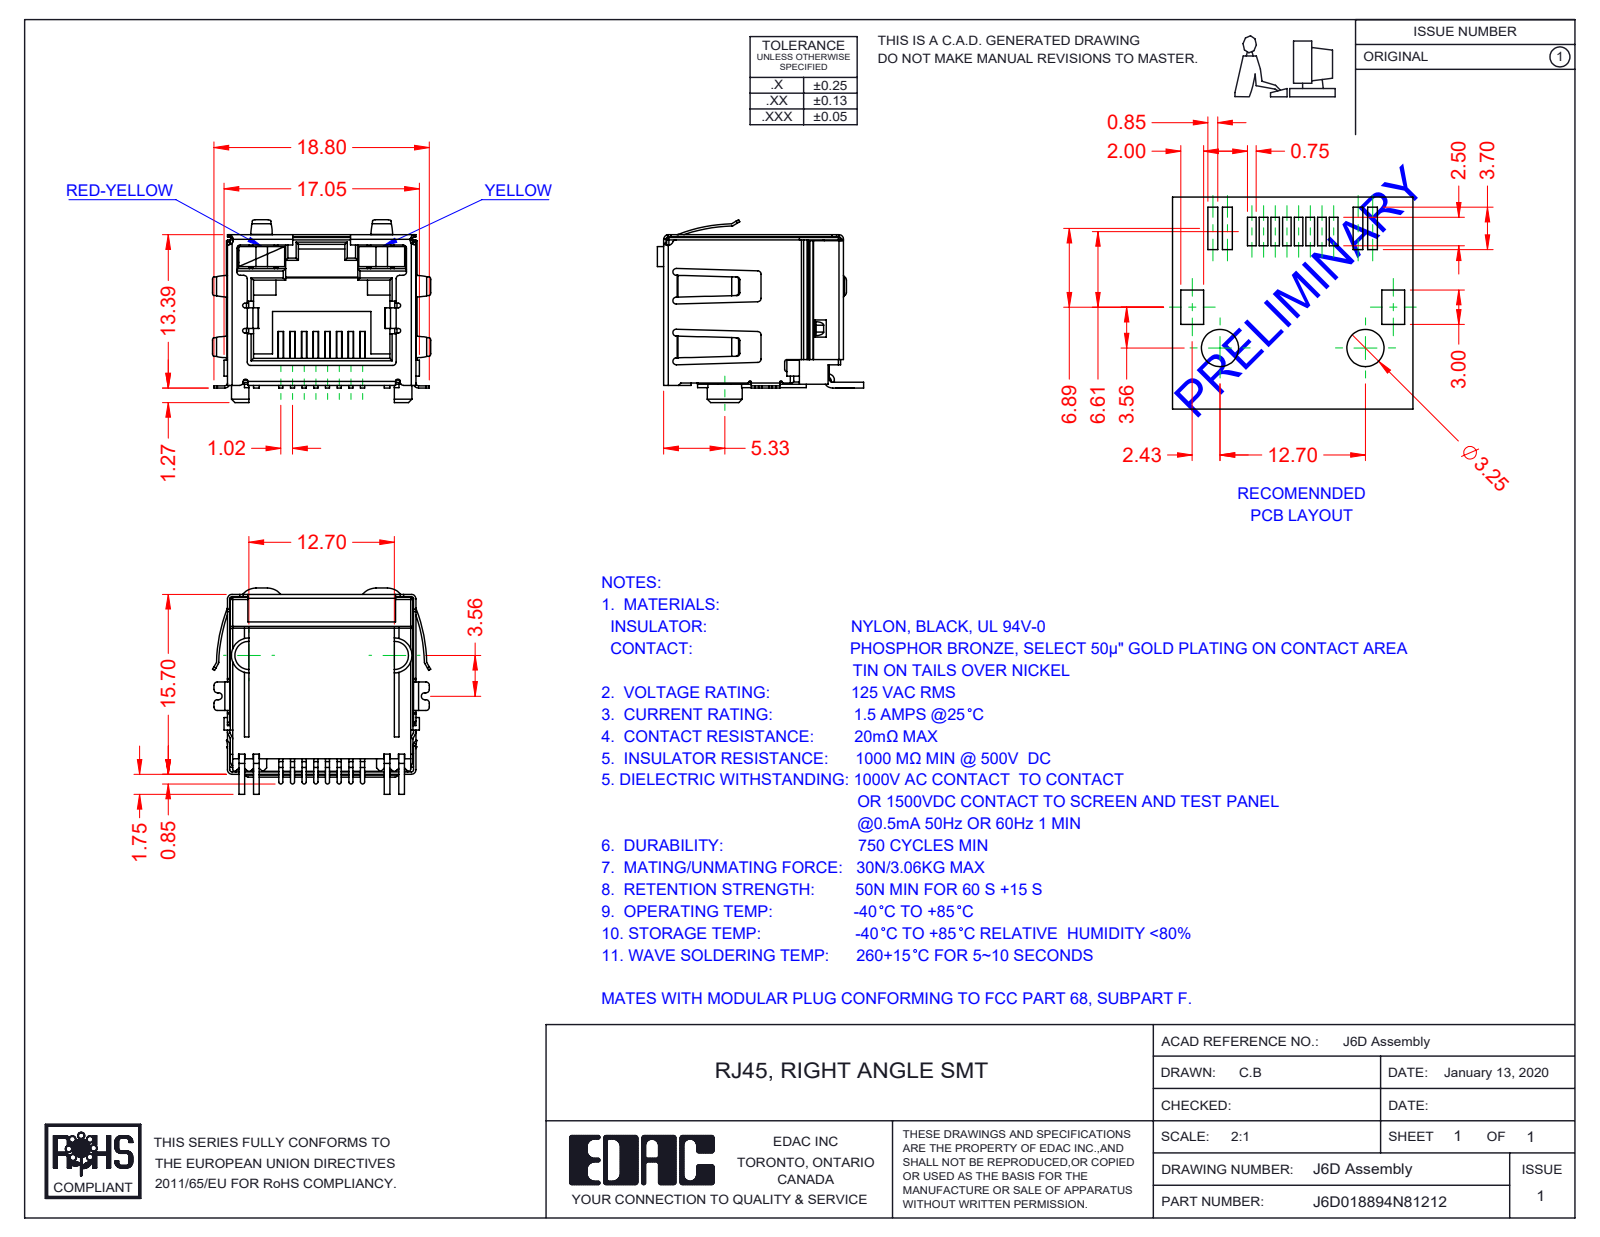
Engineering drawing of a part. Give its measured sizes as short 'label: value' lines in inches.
name: 6D Shield_LED - EMI; 6D Insulator; 6D LED LH_8-Red-Yellow; 6D LED RH_1-Yellow (+2 more)
written by: SolidWorks 2016 (CONFIG_CONTROL_DESIGN)
unit: in
bodies: 12 solids, 1031 faces (702 planar, 284 cylindrical, 45 other)
size: 0.75 × 0.709 × 0.628
volume: 0.109 in³; area: 7.434 in²
rounds: 55× R0.012, 40× R0.008, 19× R0.016, 16× R0.01, 12× R0.004, 8× R0.006, 8× R0.007, 6× R0.02
face distances: 0.63, 0.638, 0.64, 0.089, 0.039, 0.628, 0.504, 0.018, 0.514, 0.417
